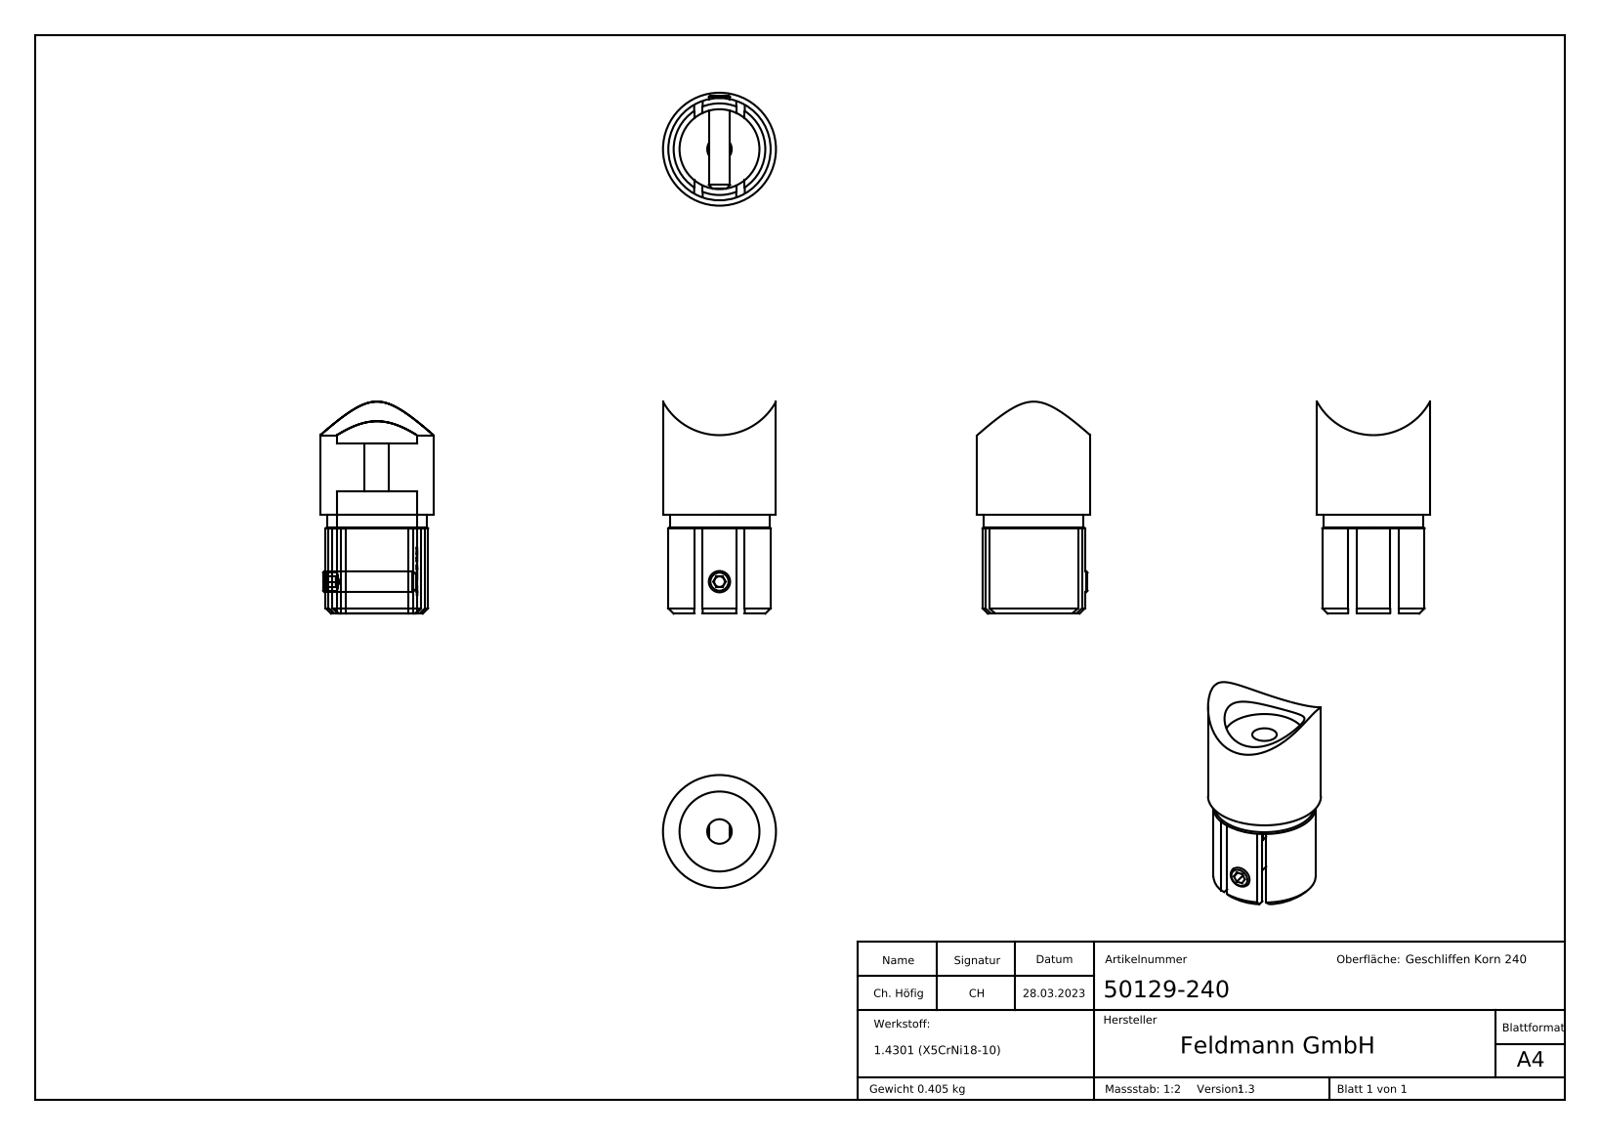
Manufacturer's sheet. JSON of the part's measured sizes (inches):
{"part_name": "5012X-240 Teil1_50129-240 Teil1; 50129-240; DIN913_DIN 913 M8x35", "step_written_by": "SolidWorks 2018 (CONFIG_CONTROL_DESIGN)", "units": "inches", "bodies": {"solids": 2, "faces": 276, "planar": 131, "cylindrical": 42, "other": 103}, "overall_size": [3.133, 1.669, 1.669], "volume_in3": 3.132, "surface_area_in2": 29.02, "round_holes": [[0.268, 1], [0.362, 1], [1.181, 1]], "round_bosses_or_shafts": [[1.669, 1], [1.512, 1], [1.472, 1], [0.315, 1]], "partial_cylinders_radius": [[0.594, 1], [0.951, 1]], "face_to_face_distances": [0.709, 0.126, 0.622, 1.063, 0.748, 0.354, 0.496, 1.457, 1.811, 2.52]}
